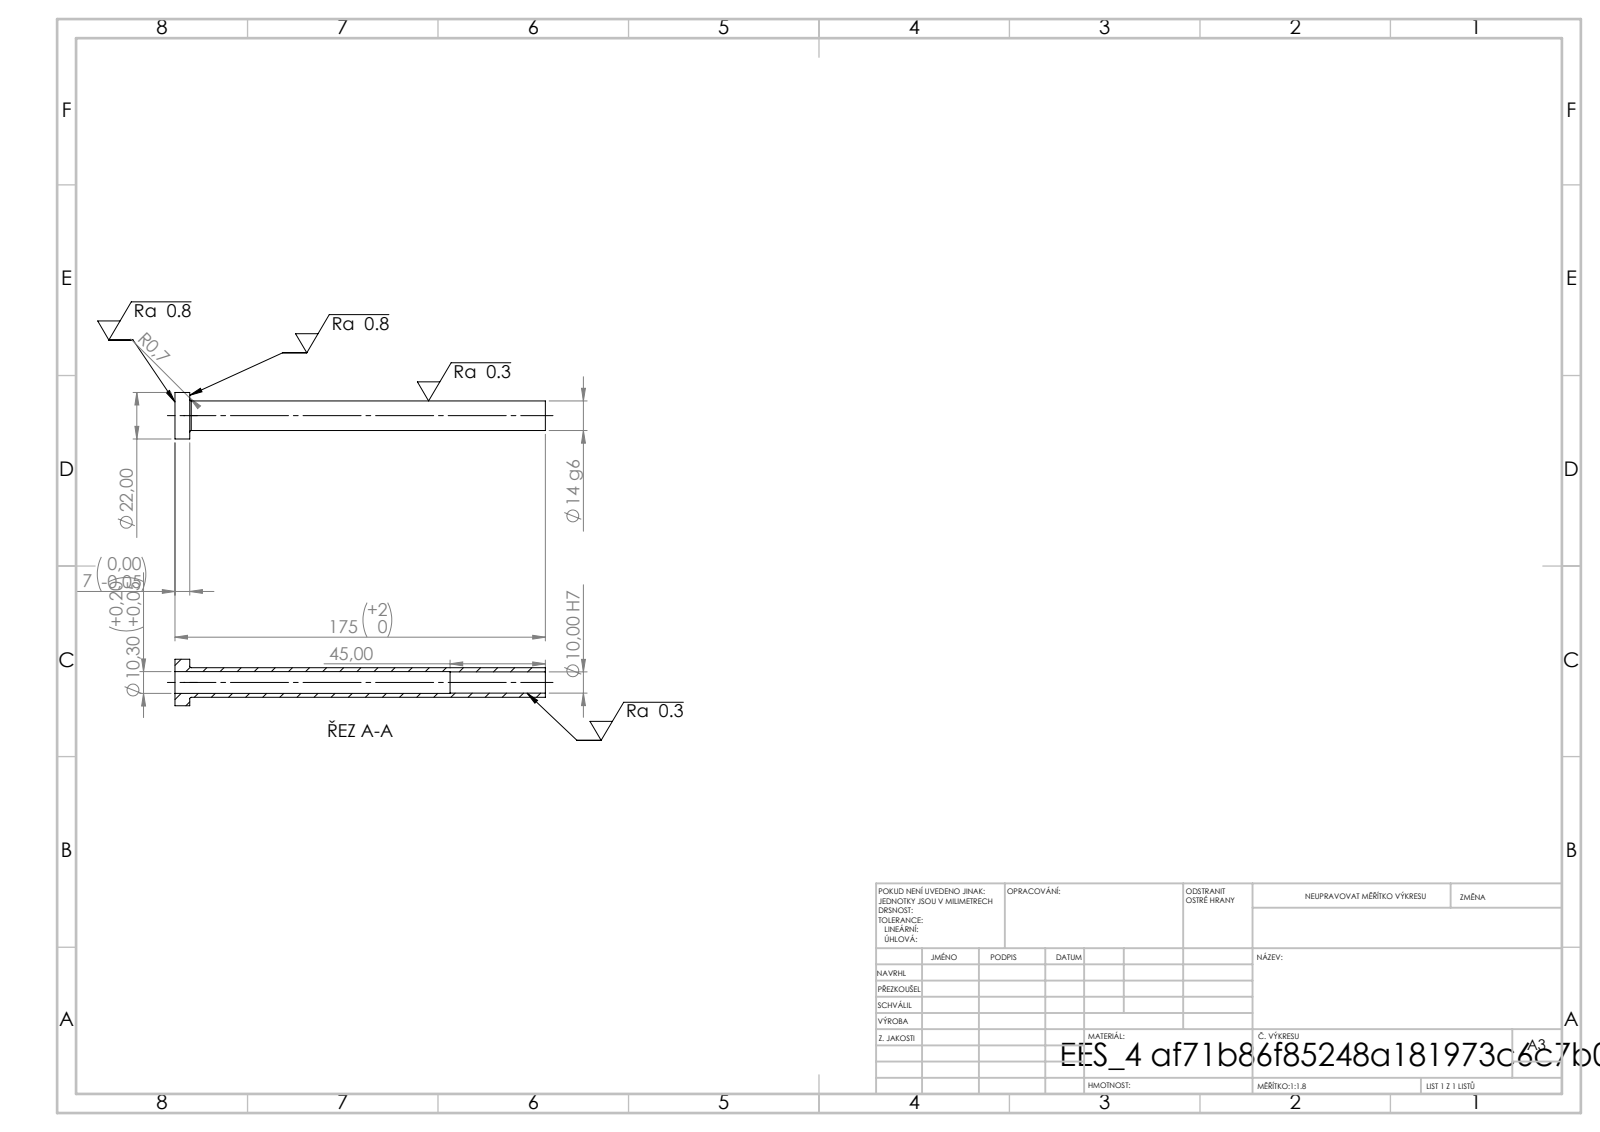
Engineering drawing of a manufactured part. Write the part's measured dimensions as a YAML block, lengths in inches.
step_written_by: "SolidWorks 2019 (CONFIG_CONTROL_DESIGN)"
units: inches
bodies: {solids: 1, faces: 14, planar: 4, cylindrical: 8, other: 2}
overall_size: [6.89, 0.866, 0.866]
volume: 0.864
surface_area: 21.83
round_holes:
  - {diameter: 0.394, count: 1}
  - {diameter: 0.406, count: 1}
round_bosses_or_shafts:
  - {diameter: 0.866, count: 1}
  - {diameter: 0.551, count: 1}
face_to_face_distances: [0.276, 6.89, 6.614, 5.118, 4.843, 1.772]
